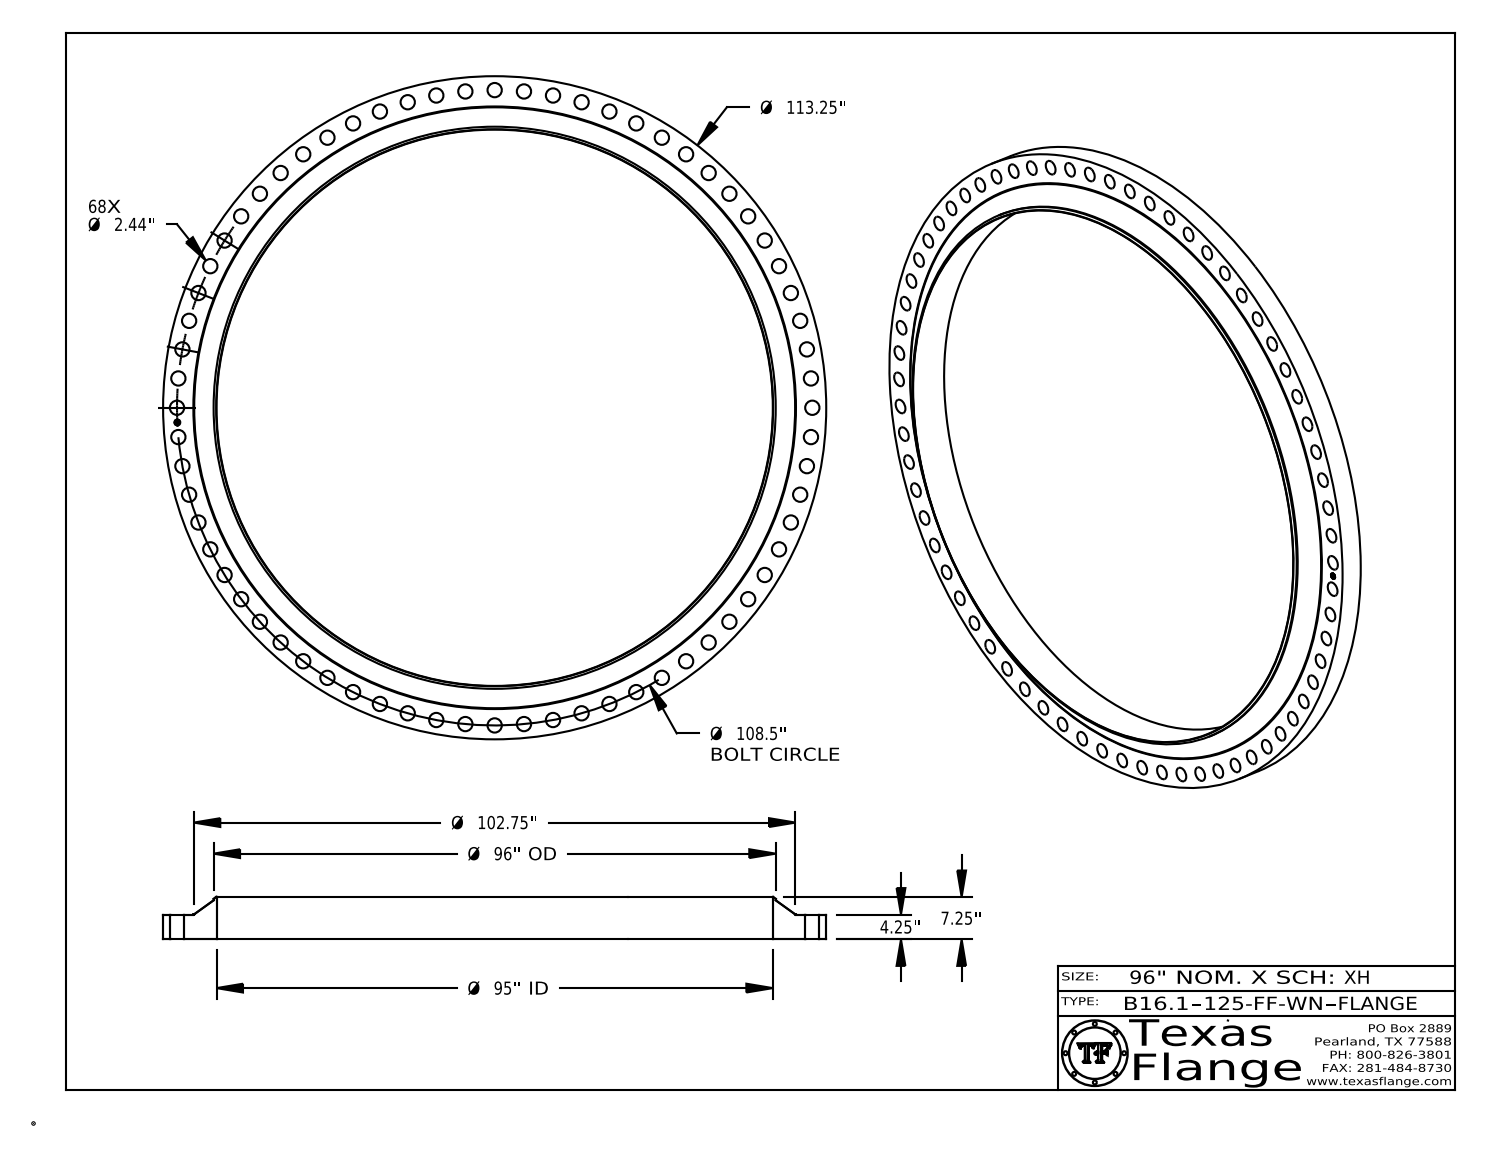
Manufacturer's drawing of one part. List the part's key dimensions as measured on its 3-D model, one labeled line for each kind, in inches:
Part name (STEP PRODUCT): B16.1, Class 125-FF-WN
STEP written by: CATIA V5 STEP AP214 (AUTOMOTIVE_DESIGN)
Units: inches
Bodies: 1 solid, 536 faces (368 planar, 162 cylindrical, 6 other)
Overall size (bounding box): 113.25 × 113.25 × 7.25
Volume: 13 028 in³ · Surface area: 11 573 in²
Round holes (diameter × count): ⌀2.44 ×68, ⌀1 ×1, ⌀95 ×1
Round bosses / shafts (diameter × count): ⌀0.061 ×8, ⌀113.25 ×1, ⌀96 ×1, ⌀0.788 ×1
Main face-to-face distances: 4.25, 7.25, 3, 4.235, 0.015, 3.015, 0.298, 0.293, 0.054, 0.193
Hole centre spacings: 54.25, 108.037, 106.653, 108.384, 14.99, 105.618, 19.937, 5.011
